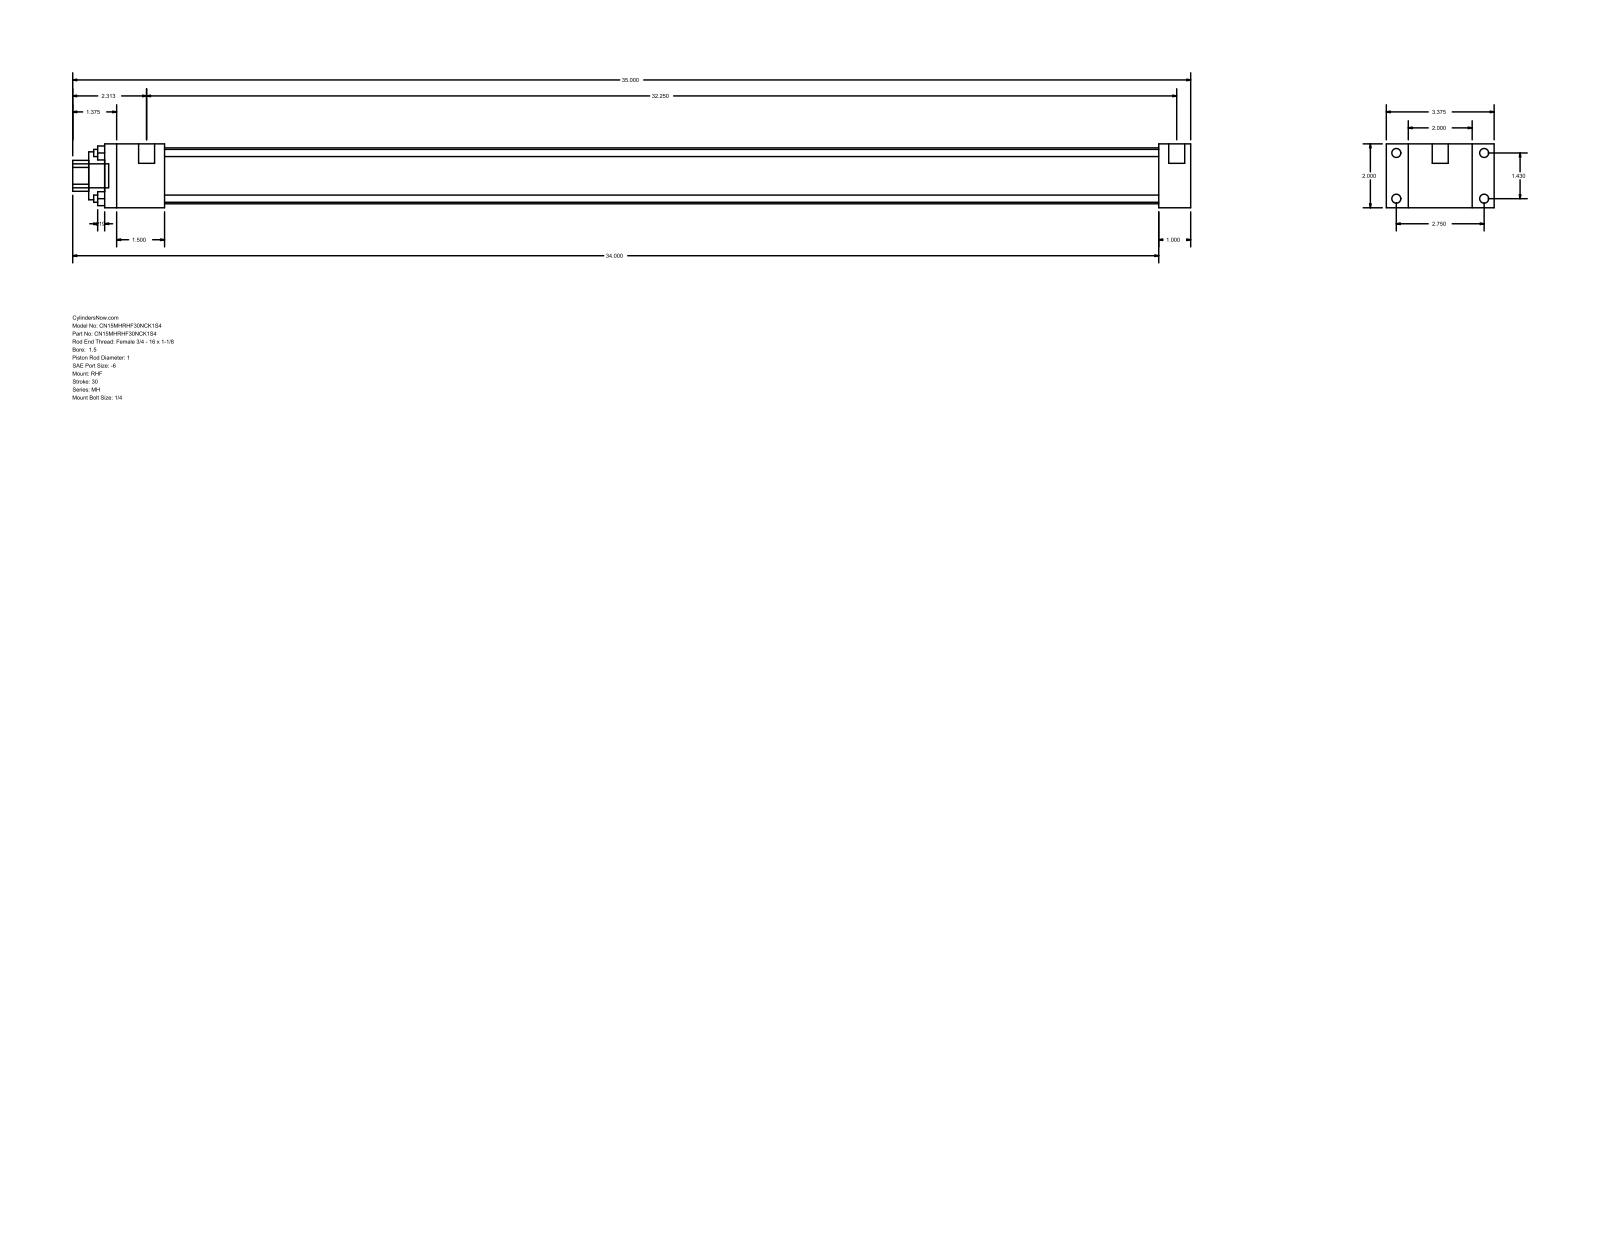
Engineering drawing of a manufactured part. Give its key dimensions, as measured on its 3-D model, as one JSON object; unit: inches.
{"part_name": "MH_RHF__0150_1", "step_written_by": "GSSL Pune (CONFIG_CONTROL_DESIGN)", "units": "inches", "bodies": {"solids": 0, "faces": 88, "planar": 60, "cylindrical": 28, "other": 0}, "overall_size": [35, 3.375, 2], "round_holes": [[0.225, 4], [1, 1], [1.5, 1], [1.75, 1]], "round_bosses_or_shafts": [[0.281, 4], [0.219, 4], [0.5, 2], [0.75, 1]], "partial_cylinders_radius": [[0.484, 1]], "face_to_face_distances": [2, 1, 0.687, 2.687, 3.375, 34, 33, 1.875, 31.125, 32.125], "hole_center_spacings": [1.011, 1.43, 2.022]}
